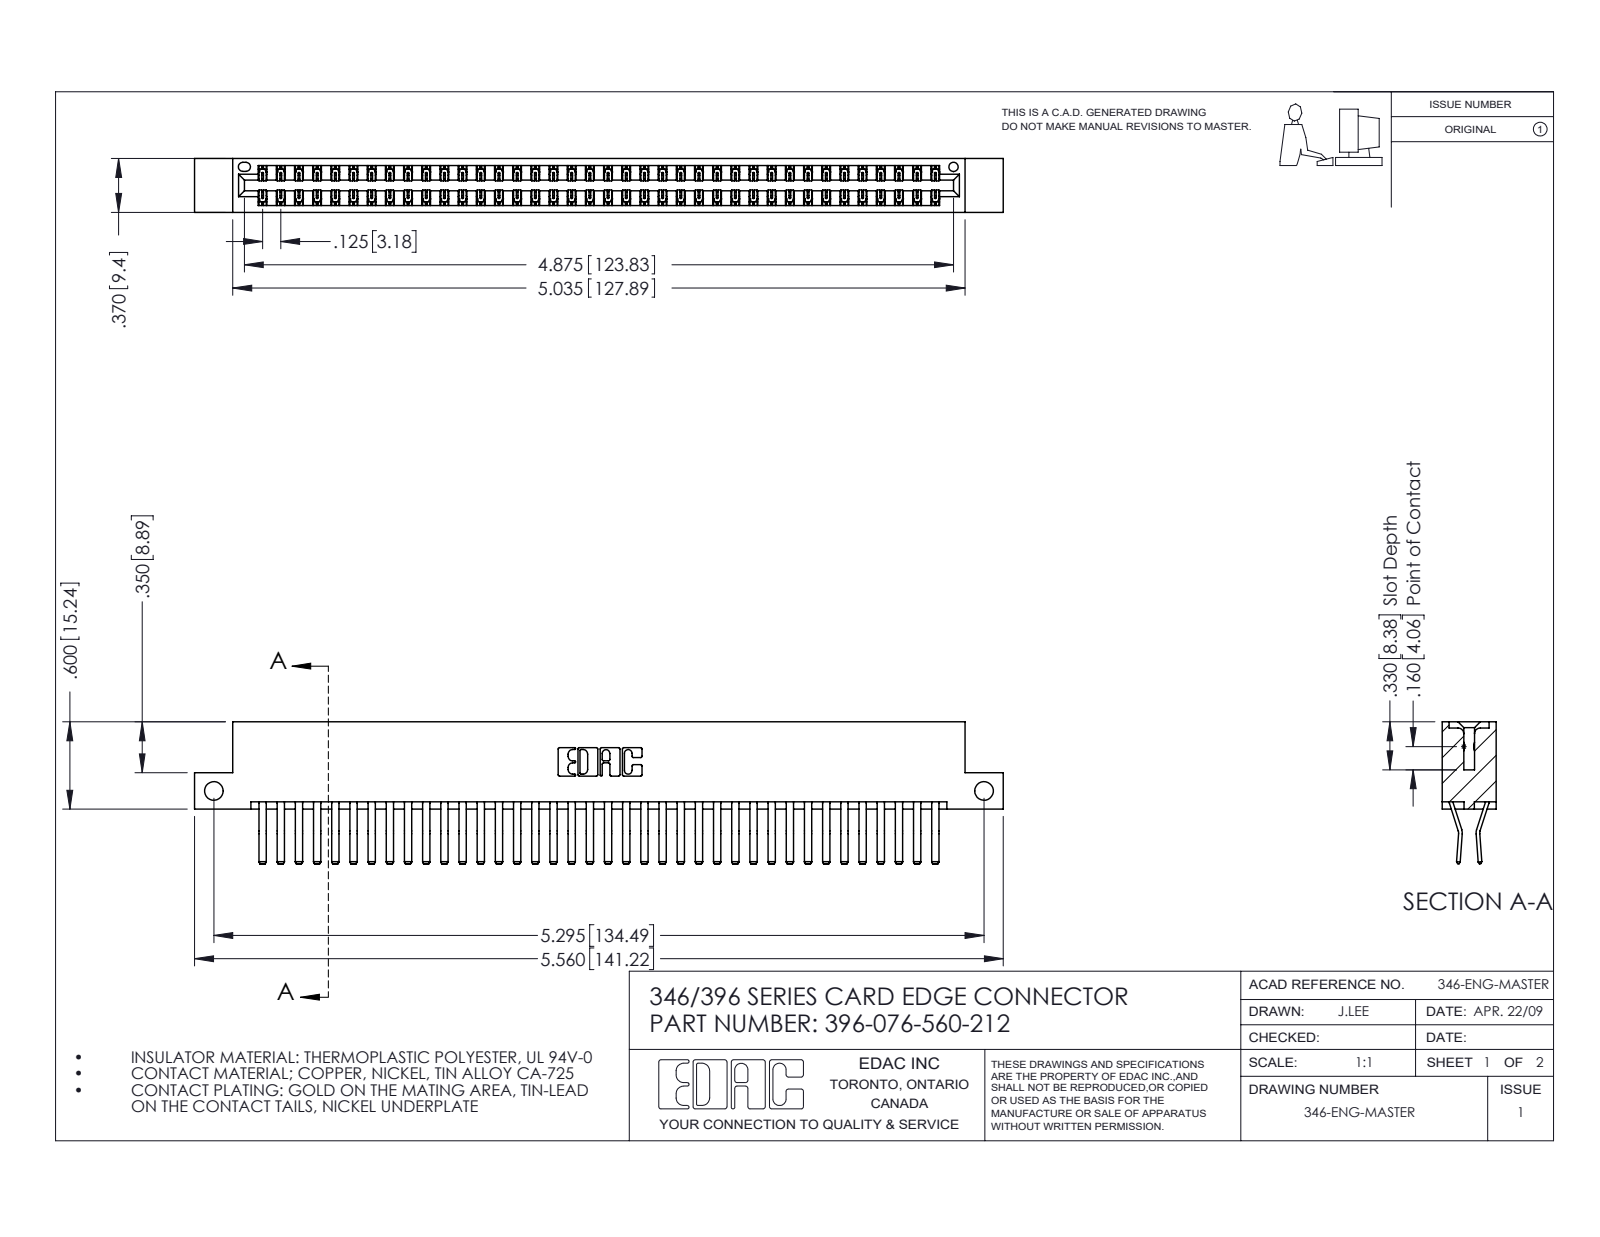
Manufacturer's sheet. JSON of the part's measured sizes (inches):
{"part_name": "396-076-560-212; 345-292-001_560 Tail; 346 Part_Flush Mounting Lugs - Side Mount", "step_written_by": "SolidWorks 2016 (CONFIG_CONTROL_DESIGN)", "units": "inches", "bodies": {"solids": 77, "faces": 4226, "planar": 2736, "cylindrical": 1490, "other": 0}, "overall_size": [5.56, 0.975, 0.37], "volume_in3": 0.864, "surface_area_in2": 31.9, "round_holes": [[0.128, 2], [0.064, 1]], "partial_cylinders_radius": [[0.006, 114], [0.01, 22], [0.007, 6], [0.031, 6], [0.026, 3], [0.01, 2], [0.014, 2], [0.022, 2]], "face_to_face_distances": [0.048, 0.322, 0.37, 0.025, 0.25, 0.072, 0.298, 0.275, 0.148, 0.222], "hole_center_spacings": [5.295]}
